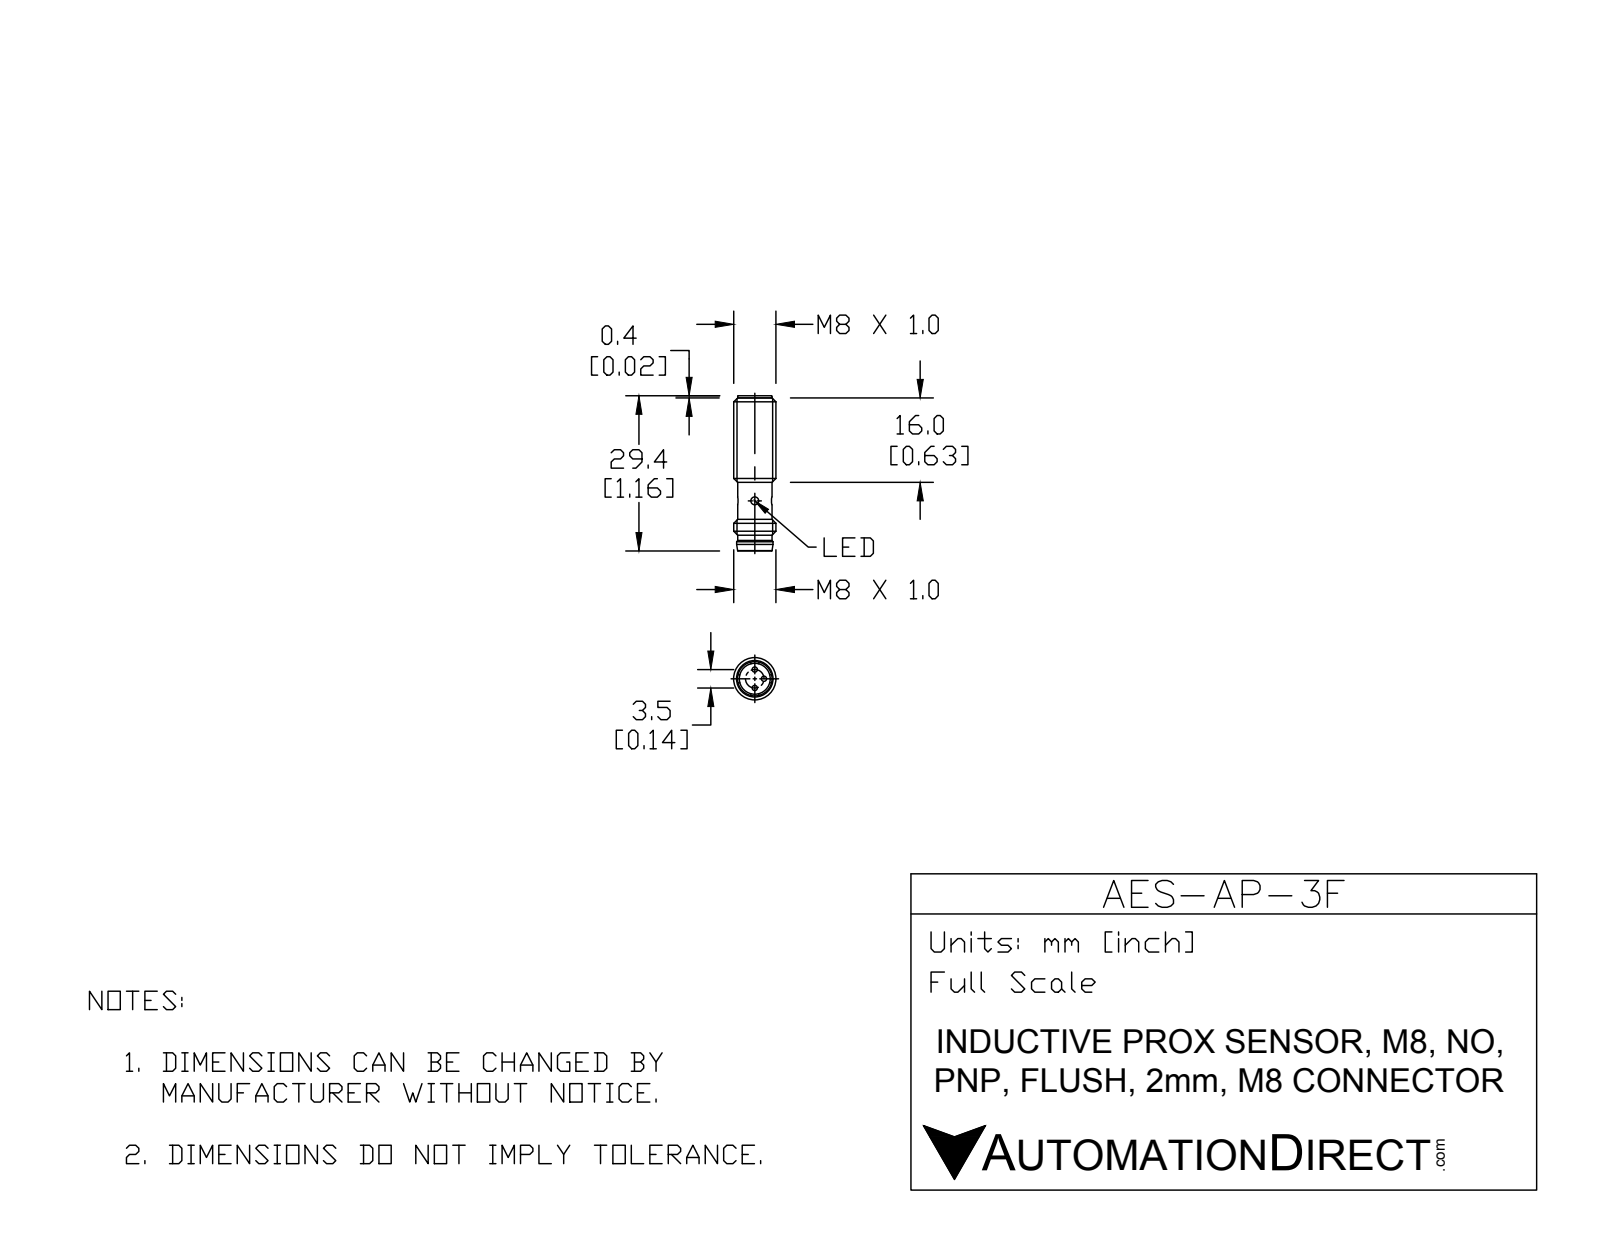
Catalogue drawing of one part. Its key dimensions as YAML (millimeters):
part_name: "AES-AP-3F"
step_written_by: "SolidWorks 2015 (CONFIG_CONTROL_DESIGN)"
units: millimeters
bodies: {solids: 1, faces: 58, planar: 10, cylindrical: 28, other: 20}
overall_size: [29.4, 8, 8]
volume: 1157
surface_area: 928
round_holes:
  - {diameter: 1.5, count: 2}
  - {diameter: 5.85, count: 1}
round_bosses_or_shafts:
  - {diameter: 1, count: 3}
  - {diameter: 8, count: 1}
  - {diameter: 6.9, count: 1}
  - {diameter: 6.5, count: 1}
face_to_face_distances: [24.4, 3, 27.4, 5.5, 11, 8, 16.4, 27, 24, 16]
